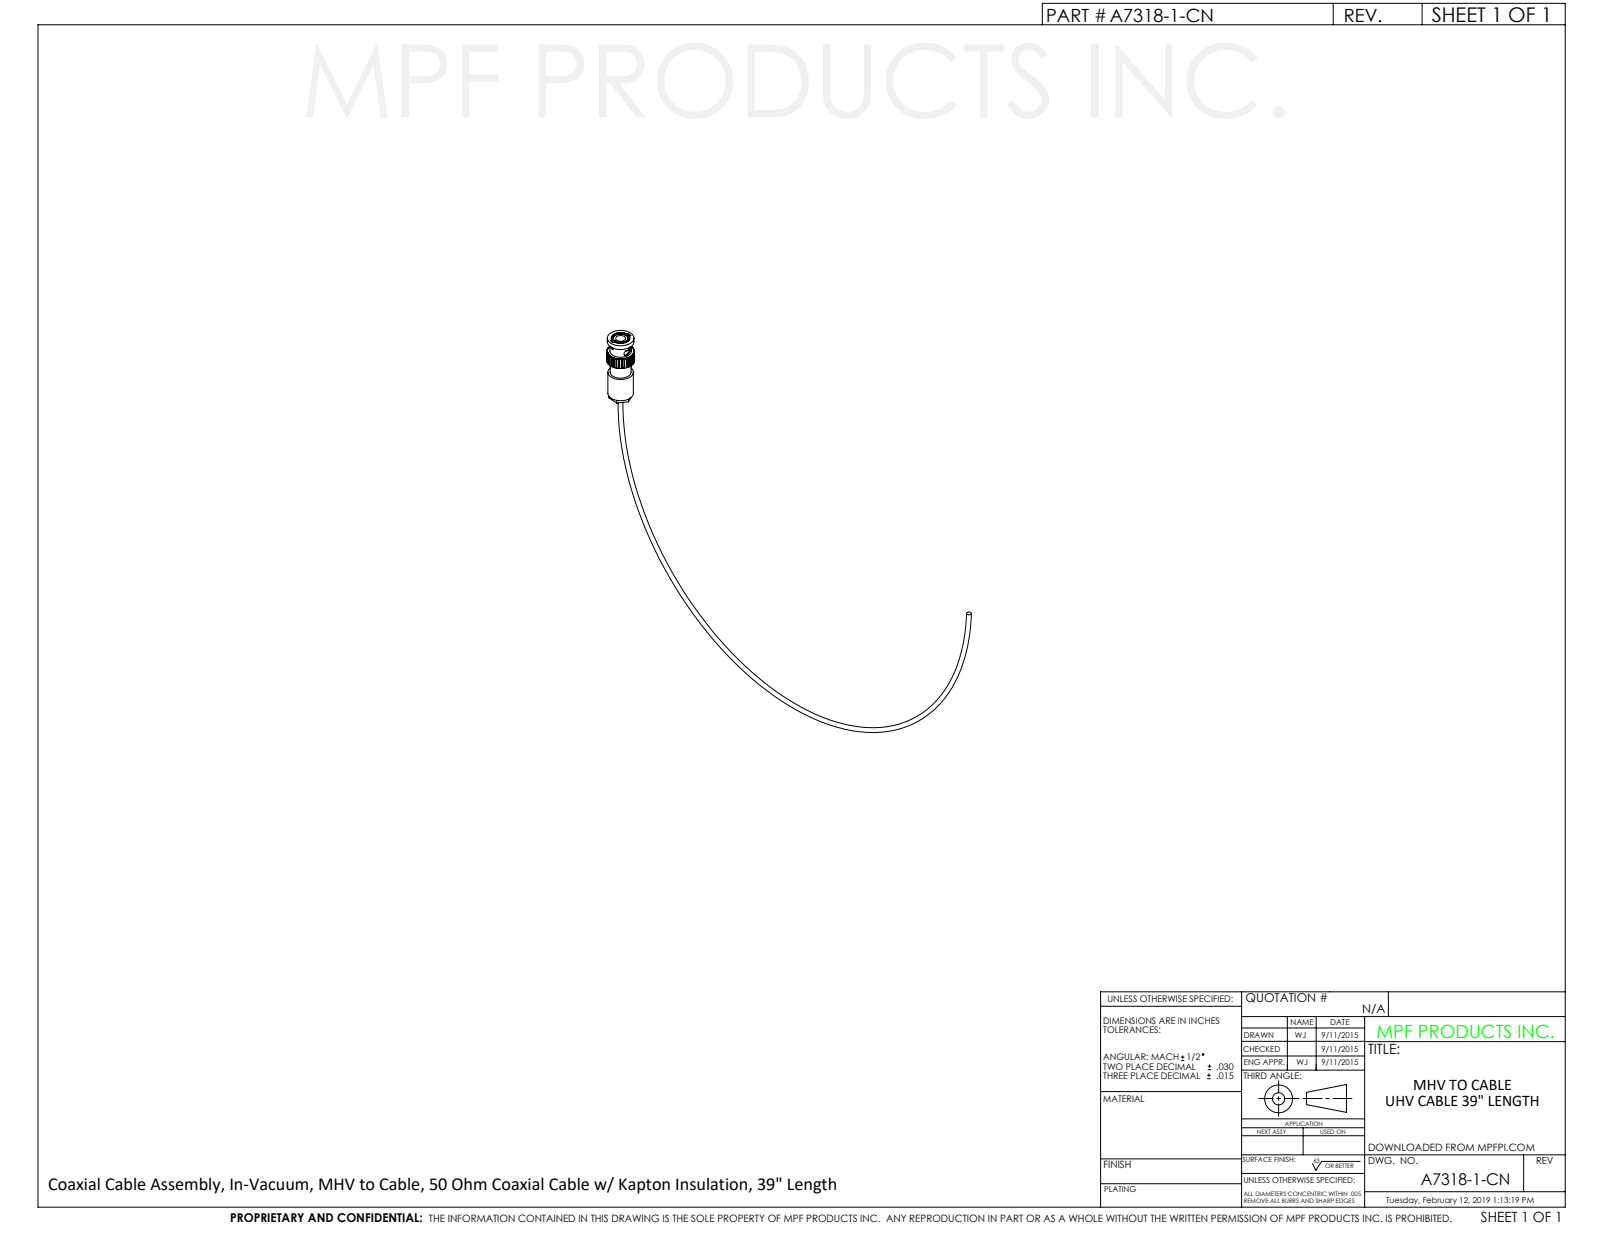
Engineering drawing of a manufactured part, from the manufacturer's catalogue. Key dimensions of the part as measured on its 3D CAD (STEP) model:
Part name (STEP PRODUCT): A7317-1-CN
STEP written by: SolidWorks 2012 (CONFIG_CONTROL_DESIGN)
Units: inches
Bodies: 2 solids, 308 faces (220 planar, 86 cylindrical, 2 other)
Overall size (bounding box): 5.924 × 3.816 × 0.575
Volume: 0.204 in³ · Surface area: 6.503 in²
Round holes (diameter × count): ⌀0.074 ×1, ⌀0.158 ×1, ⌀0.194 ×1, ⌀0.39 ×1
Round bosses / shafts (diameter × count): ⌀0.55 ×1, ⌀0.525 ×1, ⌀0.445 ×1, ⌀0.43 ×1, ⌀0.308 ×1
Partial cylindrical surfaces — rounded edges, fillets, slot ends (radius × count): R0.068 ×1, R0.15 ×1, R0.151 ×1, R0.287 ×1
Main face-to-face distances: 0.978, 0.014, 0.54, 0.653, 0.325, 0.878, 0.225, 0.1, 0.395, 0.385
